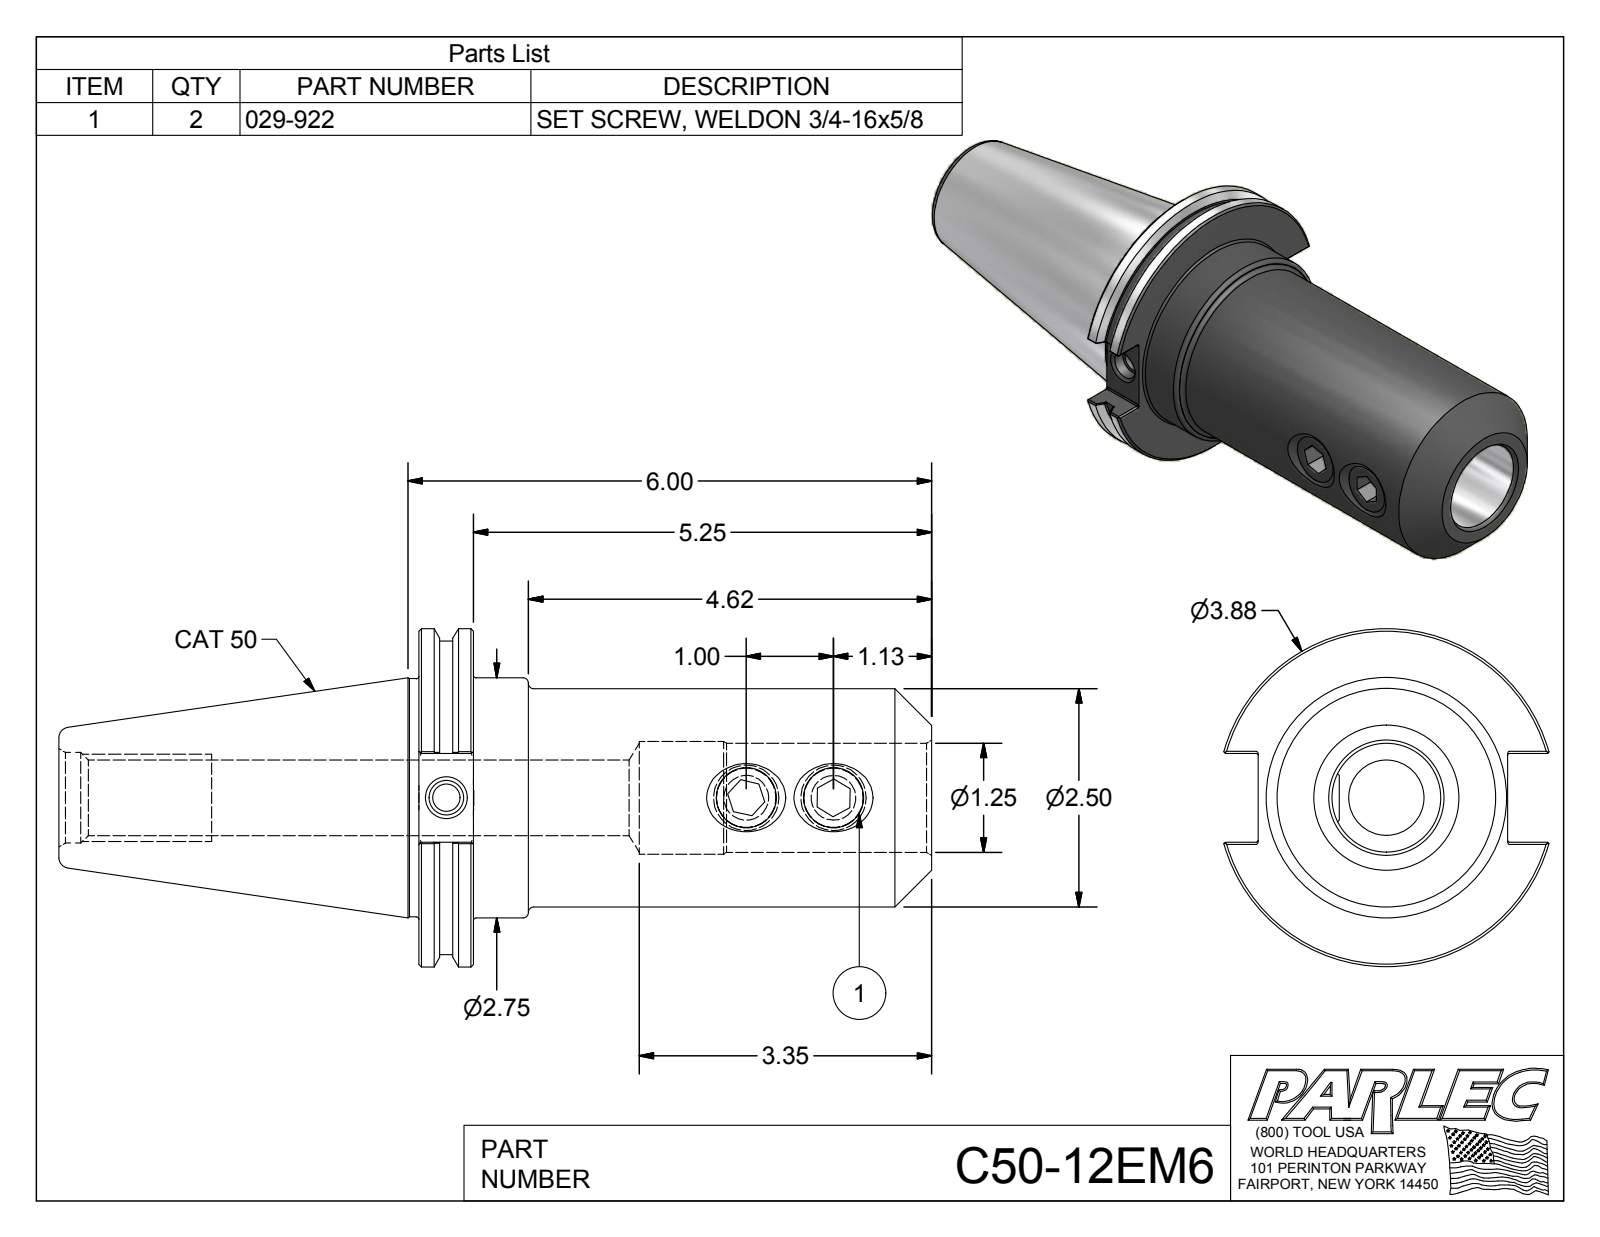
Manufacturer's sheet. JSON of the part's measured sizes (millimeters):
{"part_name": "C50-12EM6; C50-12EM6-1; 029-922", "step_written_by": "Autodesk Inventor 2012 (AUTOMOTIVE_DESIGN)", "units": "millimeters", "bodies": {"solids": 3, "faces": 119, "planar": 51, "cylindrical": 31, "other": 37}, "overall_size": [254, 98.4, 94.7], "volume_mm3": 651900, "surface_area_mm2": 84900, "round_holes": [[17.3, 2], [8, 1], [10.1, 1], [22, 1], [26.4, 1], [31.8, 1], [32.8, 1]], "round_bosses_or_shafts": [[19.1, 2], [98.4, 1], [91.3, 1], [69.9, 1], [69.3, 1], [63.5, 1]], "partial_cylinders_radius": [[0.5, 12]], "face_to_face_distances": [15.9, 149.2, 133.4, 64.9, 104.8, 120.7, 254, 72.6, 7.7, 49], "hole_center_spacings": [25.4, 87.2, 112.6]}
